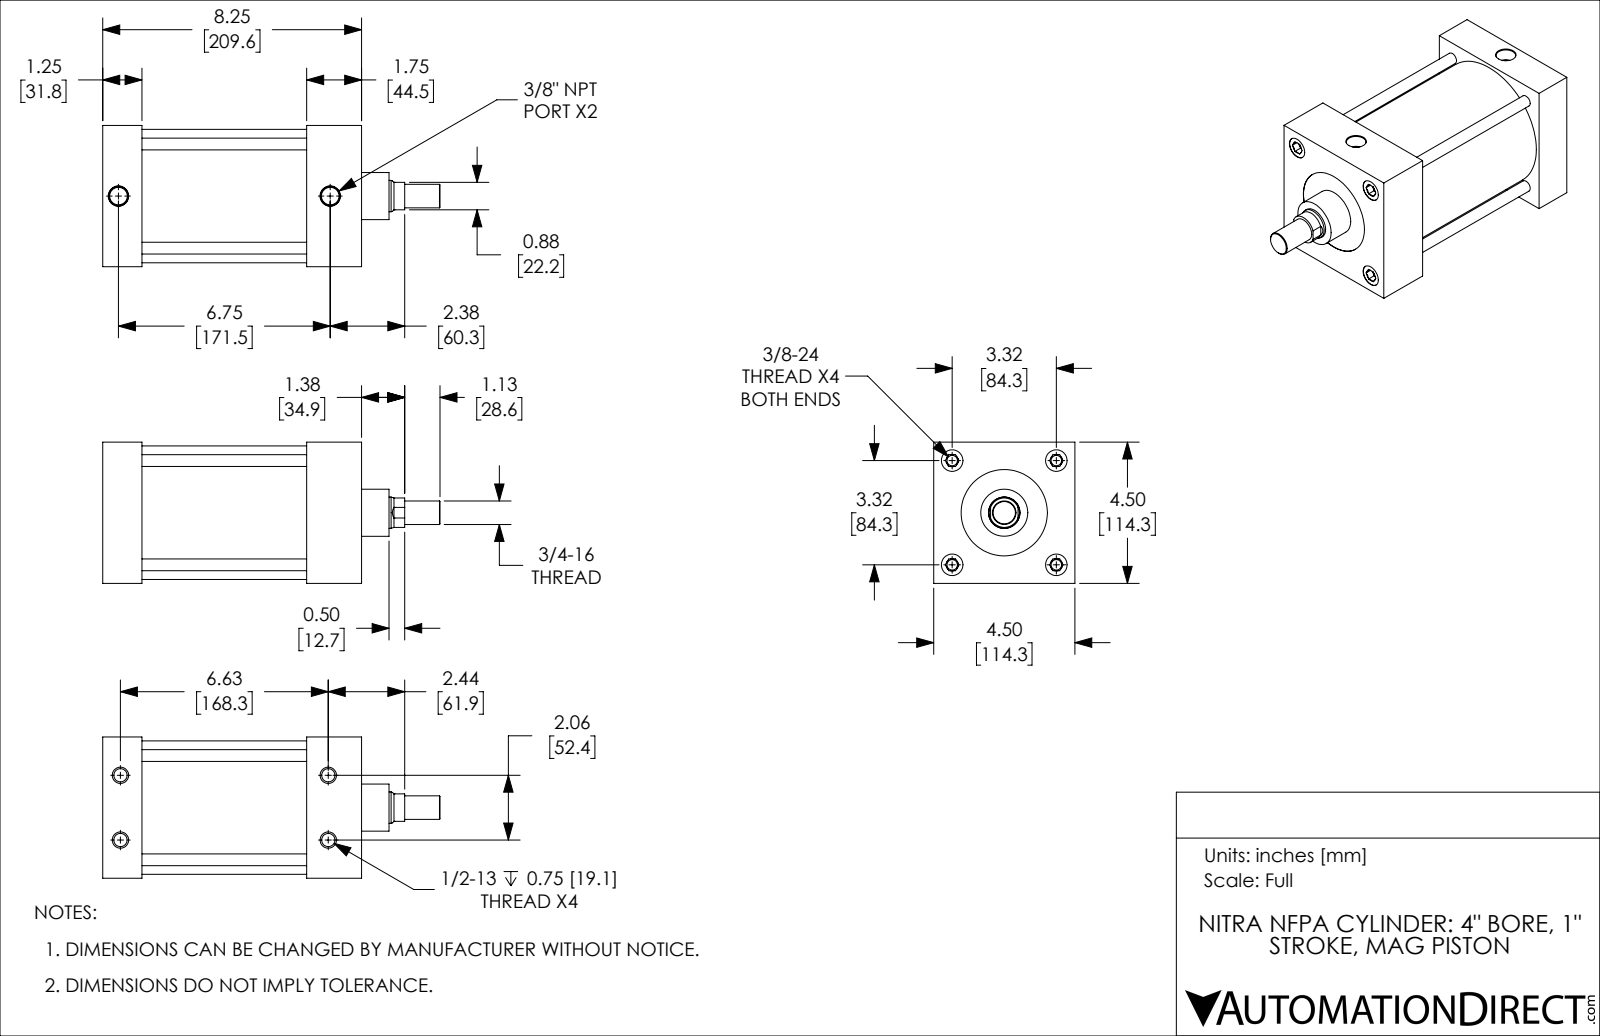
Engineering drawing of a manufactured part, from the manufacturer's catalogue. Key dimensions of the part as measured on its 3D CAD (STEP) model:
Part name (STEP PRODUCT): D264040DT-M; D264040DT-M_BODY; D264040DT-M_PISTON_KK1
STEP written by: SolidWorks 2019 (CONFIG_CONTROL_DESIGN)
Units: inches
Bodies: 2 solids, 198 faces (58 planar, 62 cylindrical, 78 other)
Overall size (bounding box): 10.75 × 4.5 × 4.5
Volume: 90.42 in³ · Surface area: 388.1 in²
Round holes (diameter × count): ⌀0.332 ×4, ⌀0.422 ×4, ⌀0.687 ×4, ⌀0.562 ×2, ⌀1.001 ×1, ⌀2.75 ×1, ⌀4.001 ×1
Round bosses / shafts (diameter × count): ⌀0.375 ×4, ⌀4.251 ×1, ⌀3.999 ×1, ⌀1.5 ×1, ⌀0.999 ×1, ⌀0.75 ×1
Partial cylindrical surfaces — rounded edges, fillets, slot ends (radius × count): R0.469 ×1
Main face-to-face distances: 1.25, 4.5, 6.5, 5.25, 8.25, 7, 1.75, 2.5, 4, 5.75
Hole centre spacings: 2.347, 3.32, 6.767, 1.033, 4.695, 6.625, 1.034, 2.062
